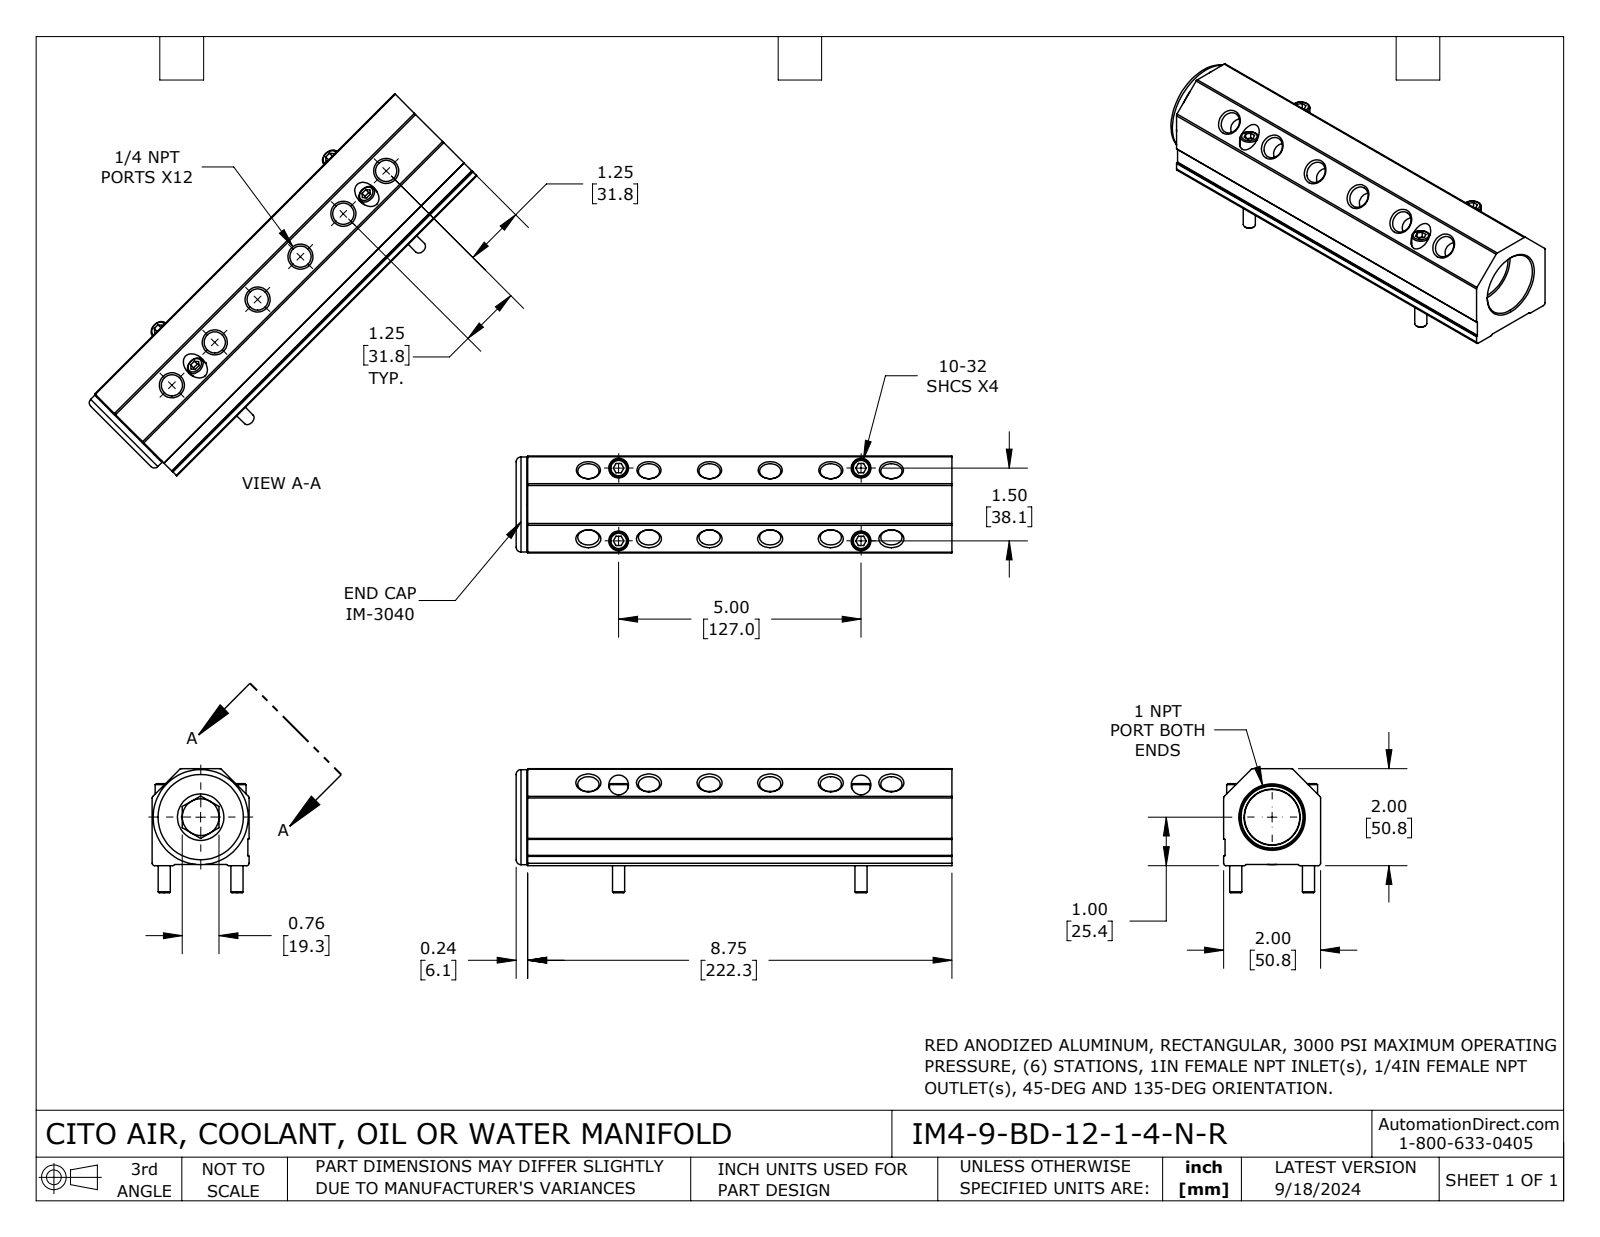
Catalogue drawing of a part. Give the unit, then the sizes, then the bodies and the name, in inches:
Units: inches
Overall size (bounding box): 8.99 × 2.56 × 2
Round holes (diameter × count): ⌀0.437 ×12, ⌀0.266 ×4, ⌀0.406 ×4, ⌀0.758 ×1, ⌀1.156 ×1, ⌀1.637 ×1
Round bosses / shafts (diameter × count): ⌀0.375 ×4, ⌀0.25 ×4, ⌀1.96 ×1, ⌀1.359 ×1, ⌀1.293 ×1, ⌀1.14 ×1
Partial cylindrical surfaces — rounded edges, fillets, slot ends (radius × count): R0.05 ×8, R0.01 ×4
Main face-to-face distances: 2, 1.975, 0.025, 0.028, 1.972, 8.75, 0.24, 8.99, 0.764, 0.524
Hole centre spacings: 1.25, 2.5, 3.75, 5, 1.5, 5.22, 6.25
Volume: 22.37 in³ · Surface area: 130.4 in²
Bodies: 6 solids, 229 faces (81 planar, 82 cylindrical, 66 other)
Part name (STEP PRODUCT): IM4-9-BD-12-1-4-N-R
STEP written by: SolidWorks 2023 (CONFIG_CONTROL_DESIGN)
